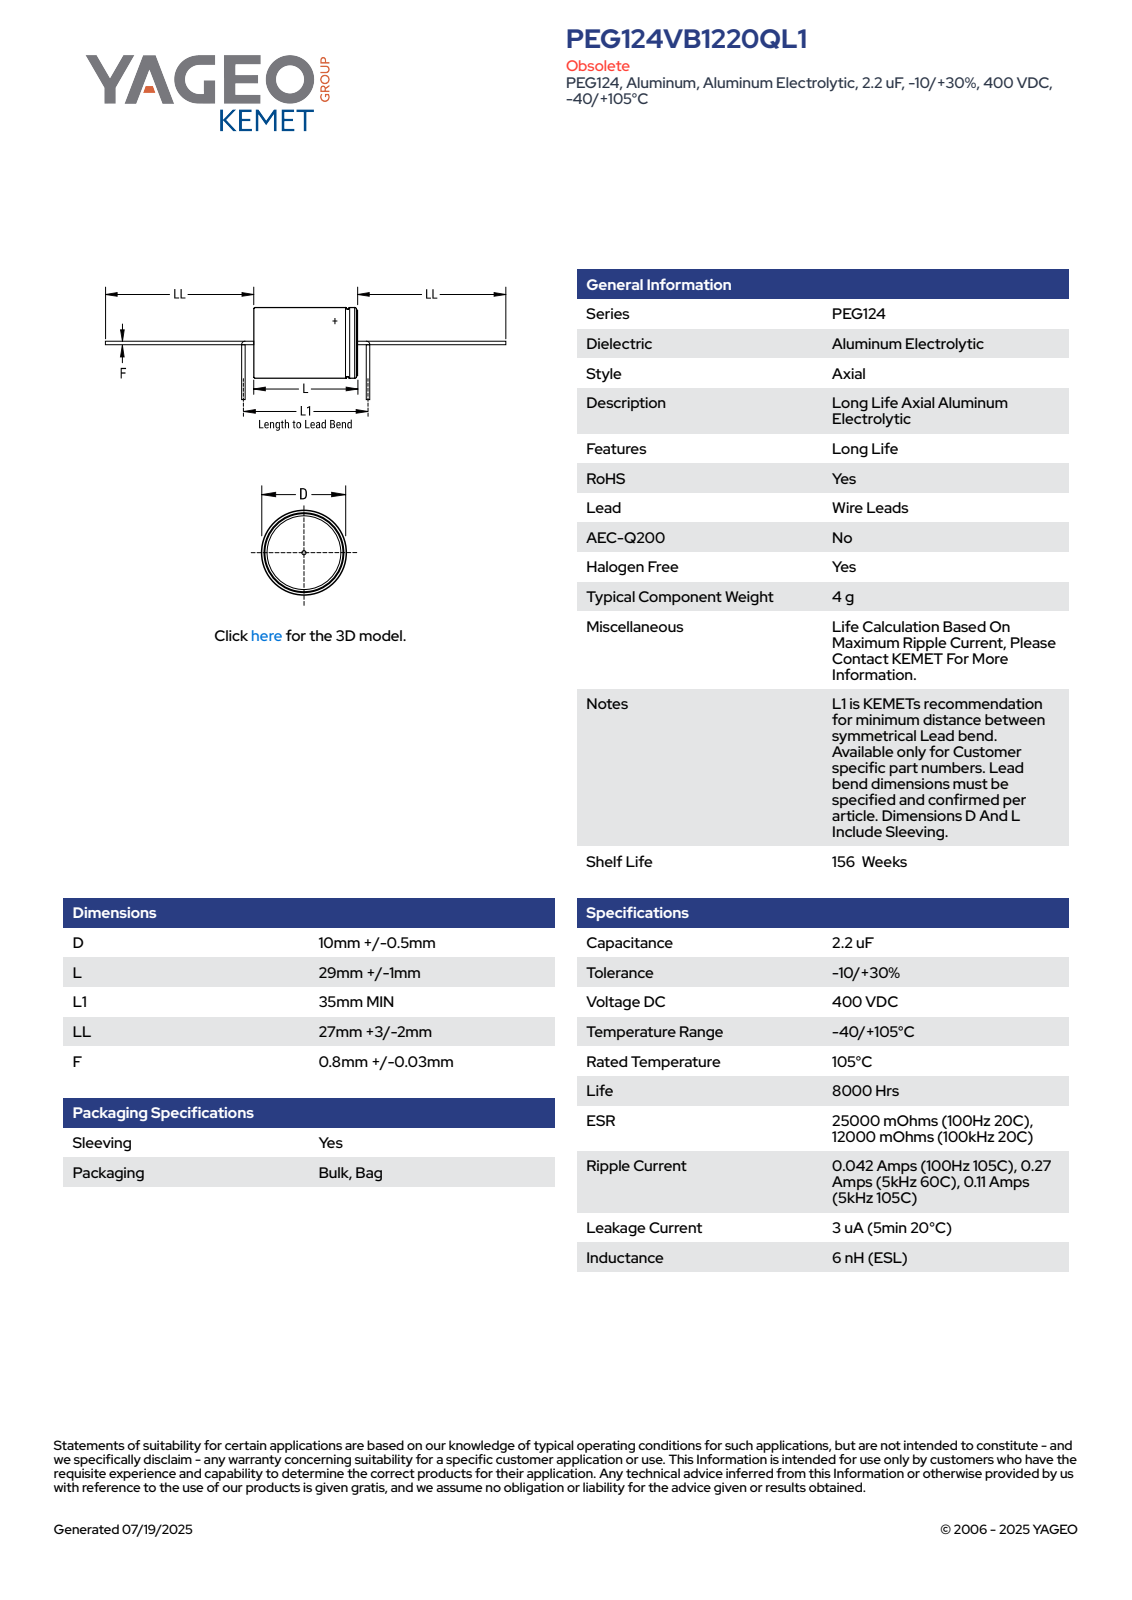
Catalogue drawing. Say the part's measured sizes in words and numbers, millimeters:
The part is named "CAA_PEG124_10X29_D10.5L30LL30F0.83". Its 3-D file was written by "SolidWorks 2014 (AUTOMOTIVE_DESIGN)". It is 1 solid with 99 faces: 27 planar, 29 cylindrical and 43 other. Overall it measures 102 by 10.5 by 10.5 millimeters. Its volume is 2 561 cubic millimeters and its surface area 1 385 square millimeters. Round holes: 1 of diameter 9.5. Round bosses or shafts: 1 of diameter 10.5, 1 of diameter 10, 1 of diameter 0.83. Partial cylindrical surfaces (rounded edges, fillets, slot ends): 1 of radius 5.24. The main face-to-face distances are 29, 30, 1, 59, 60, 102, 72, 43, 42.
